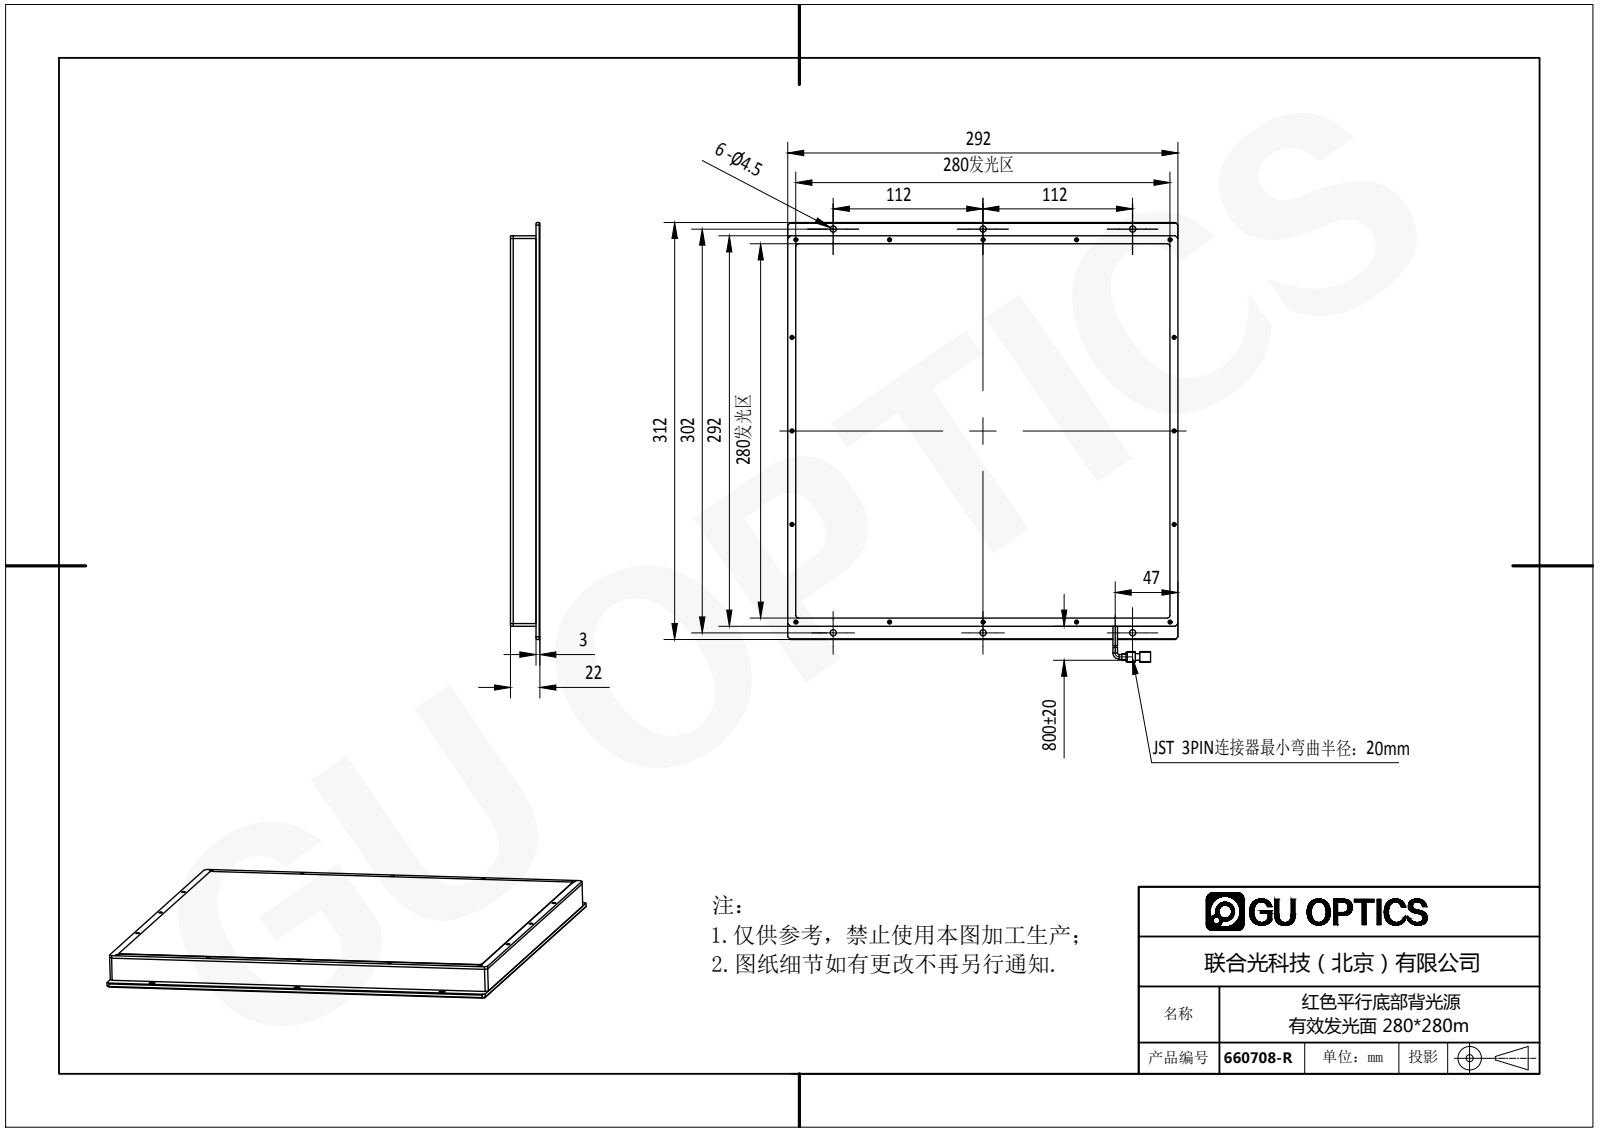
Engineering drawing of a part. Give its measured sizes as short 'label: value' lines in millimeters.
name: 660708-R
written by: SolidWorks 2016 (AUTOMOTIVE_DESIGN)
unit: mm
bodies: 5 solids, 652 faces (220 planar, 274 cylindrical, 158 other)
size: 329 × 292 × 22.1
volume: 564 669 mm³; area: 413 343 mm²
holes: 32× ⌀1.6, 16× ⌀1.25, 16× ⌀1.5, 16× ⌀2, 16× ⌀2.4, 16× ⌀2.8, 6× ⌀4.5
bosses: 2× ⌀3.5
rounds: 8× R0.5, 8× R1, 6× R2
face distances: 17, 3, 20, 19.1, 22.1, 2.1, 6, 286, 292, 280
hole spacings: 296.98, 80, 286, 105.54, 160, 184.44, 210, 264
